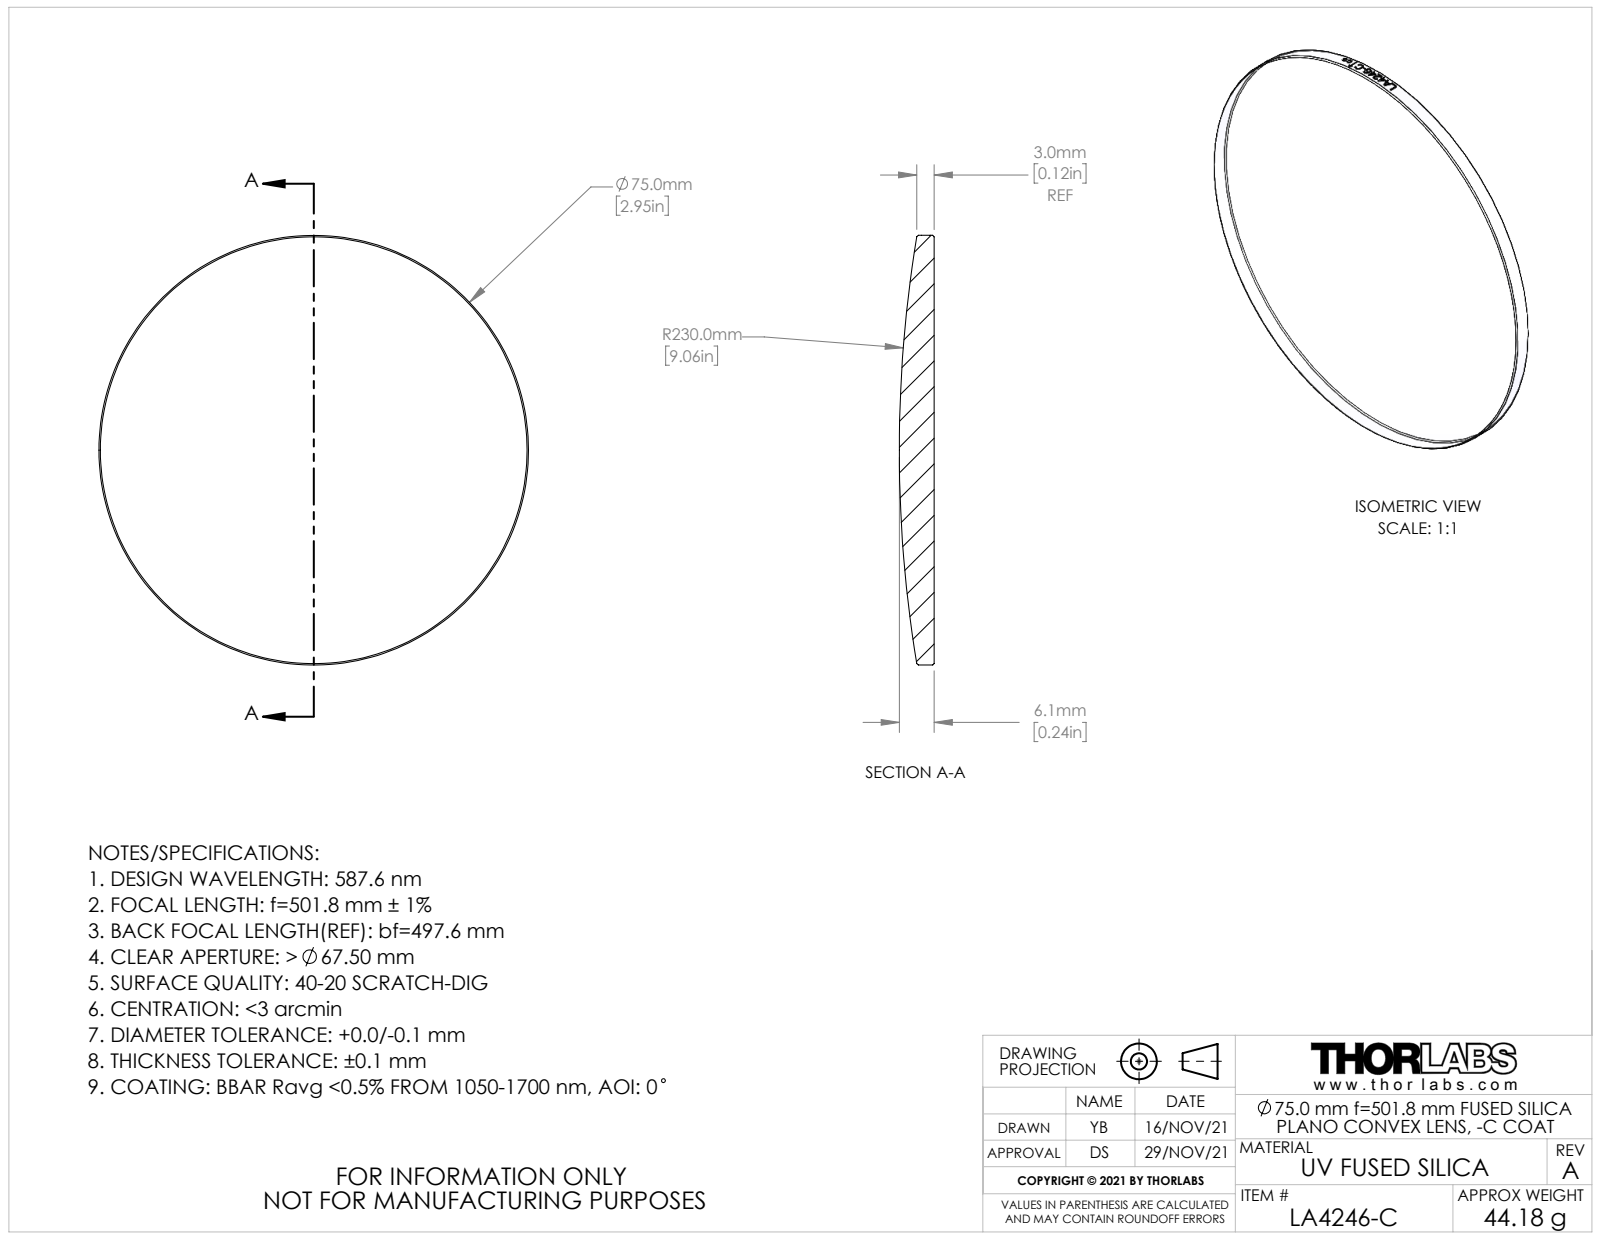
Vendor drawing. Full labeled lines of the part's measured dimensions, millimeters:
Part name (STEP PRODUCT): CTN018088-E0W; CTN018155
STEP written by: SolidWorks 2018 (AUTOMOTIVE_DESIGN)
Units: millimetres
Bodies: 1 solid, 25 faces (1 planar, 18 cylindrical, 6 other)
Overall size (bounding box): 75 × 75 × 6.08
Volume: 20 056 mm³ · Surface area: 9 510 mm²
Round bosses / shafts (diameter × count): ⌀75 ×1
